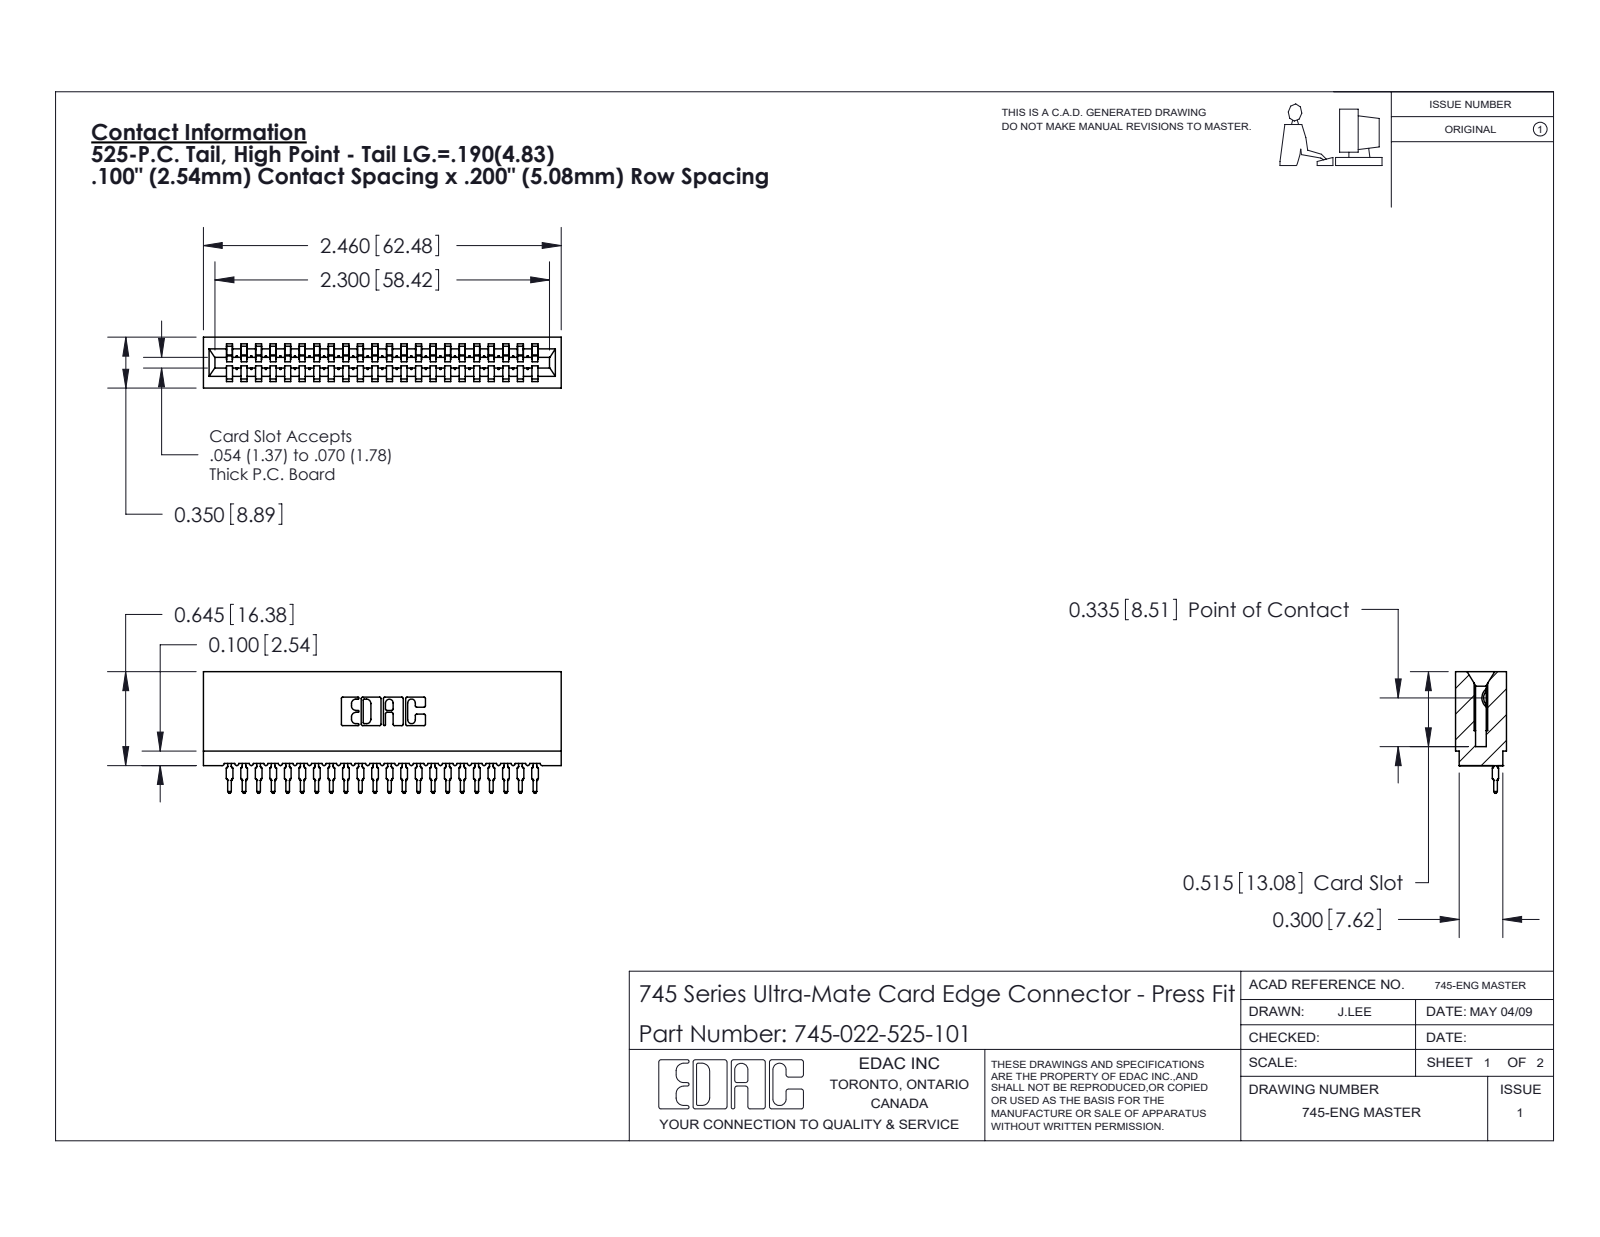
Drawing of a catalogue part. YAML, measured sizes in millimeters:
part_name: "745 Part_Insulator Option - 01; 745-022-525-101; 745-292-001_525"
step_written_by: "SolidWorks 2020 (CONFIG_CONTROL_DESIGN)"
units: millimeters
bodies: {solids: 23, faces: 2559, planar: 1529, cylindrical: 458, other: 572}
overall_size: [62.5, 21.2, 8.9]
volume: 5520
surface_area: 9858
partial_cylinders:
  - {radius: 0.4, count: 44}
  - {radius: 0.5, count: 44}
  - {radius: 0.3, count: 22}
  - {radius: 0.2, count: 6}
  - {radius: 0.8, count: 6}
  - {radius: 0.1, count: 4}
  - {radius: 0.3, count: 4}
  - {radius: 0.7, count: 3}
face_to_face_distances: [2.5, 5.1, 8.9, 3.5, 5.4, 10.2, 7.6, 1.1, 7.7, 2.4]
